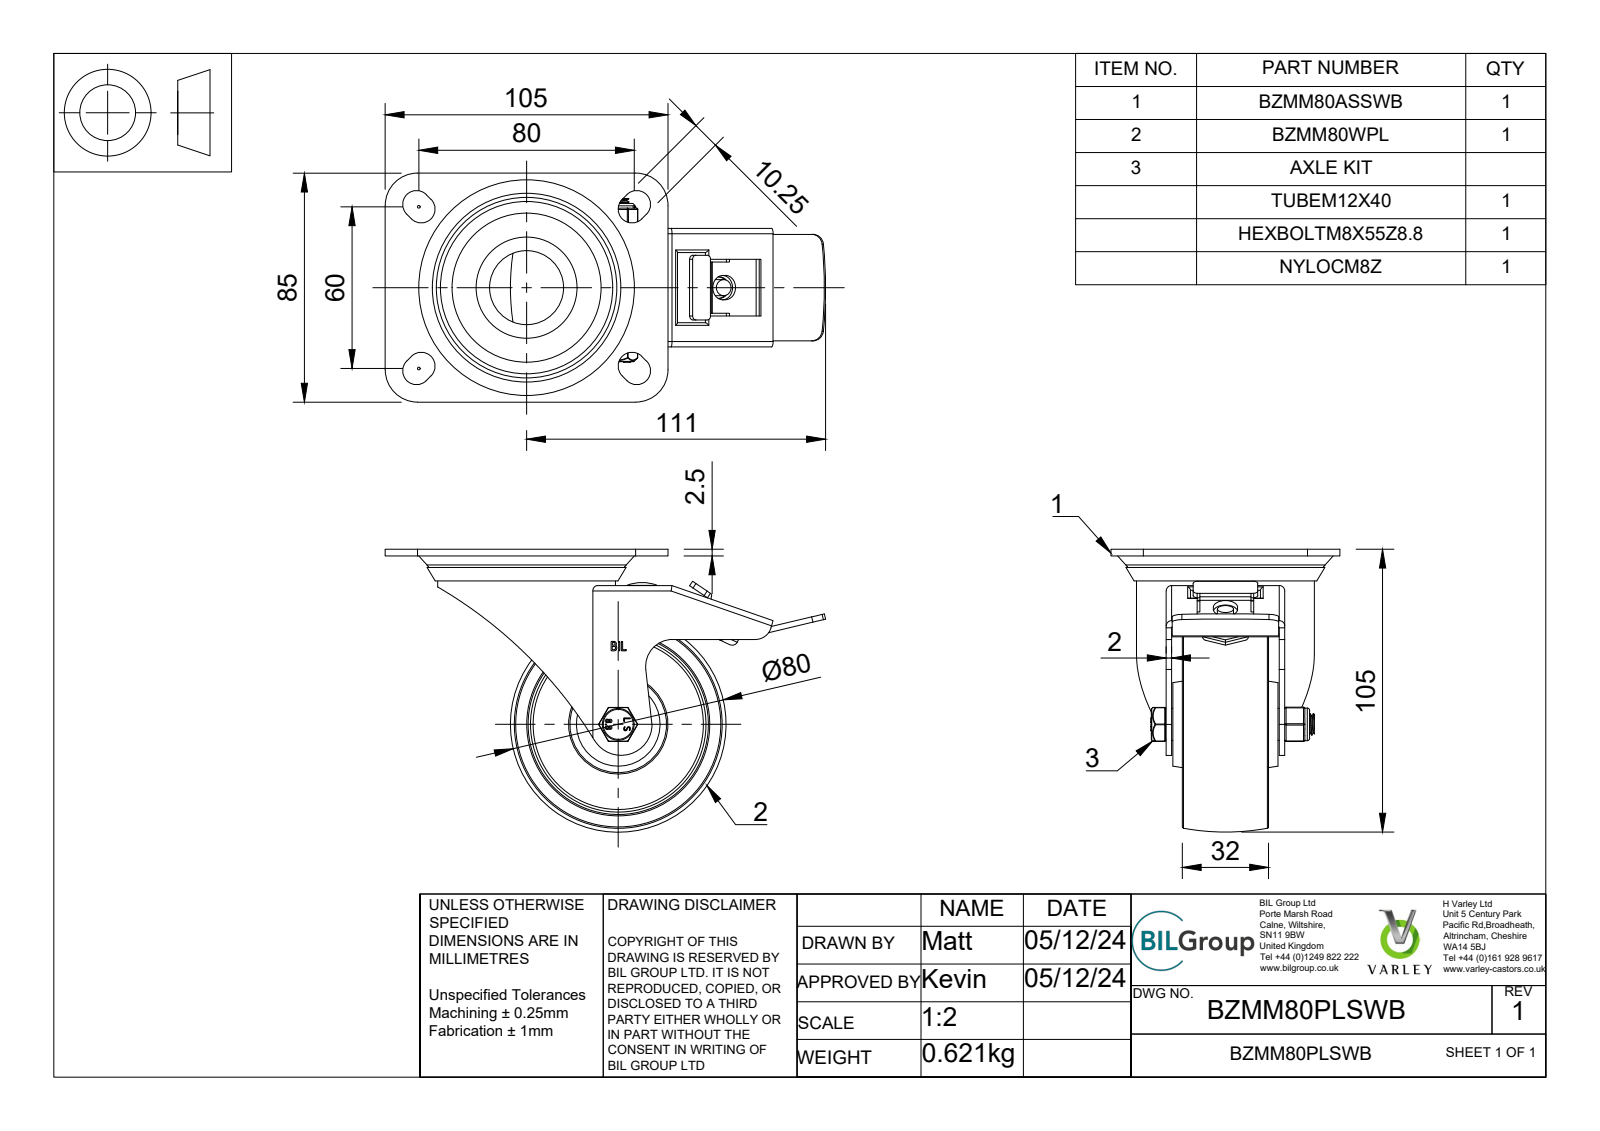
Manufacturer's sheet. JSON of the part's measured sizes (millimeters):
{"part_name": "BZMM80PLSWB v3; BZMM80ASSWB v1; ZINC PLATED, PRESSED STEEL TOP PLATE; ZINC PLATED, PRESSED STEEL TOP PLATE Geometry (+7 more)", "step_written_by": "Autodesk Translation Framework v13.20.0.188 (AP242_MANAGED_MODEL_BASED_3D_ENGINEERING_MIM_LF)", "units": "millimeters", "bodies": {"solids": 37, "faces": 593, "planar": 291, "cylindrical": 178, "other": 124}, "overall_size": [163.5, 105, 85], "volume_mm3": 165642, "surface_area_mm2": 95156, "round_holes": [[0.66, 2], [8, 2], [6, 1], [8.2, 1], [8.4, 1], [8.6, 1], [12.2, 1], [27.5, 1], [56, 1], [62, 1]], "round_bosses_or_shafts": [[66, 1], [31.5, 1], [12.1, 1], [11.9, 1], [11.5, 1], [7.87, 1], [6.45, 1], [6, 1]], "partial_cylinders_radius": [[0.5, 24], [1, 14], [0.25, 12], [2, 11], [5.12, 8], [0.33, 4], [0.64, 4], [1.5, 4]], "face_to_face_distances": [2, 2.5, 16.5, 0.5, 18.5, 25.5, 42, 23.5, 13, 6], "hole_center_spacings": [3.22, 2.49, 42.86]}
